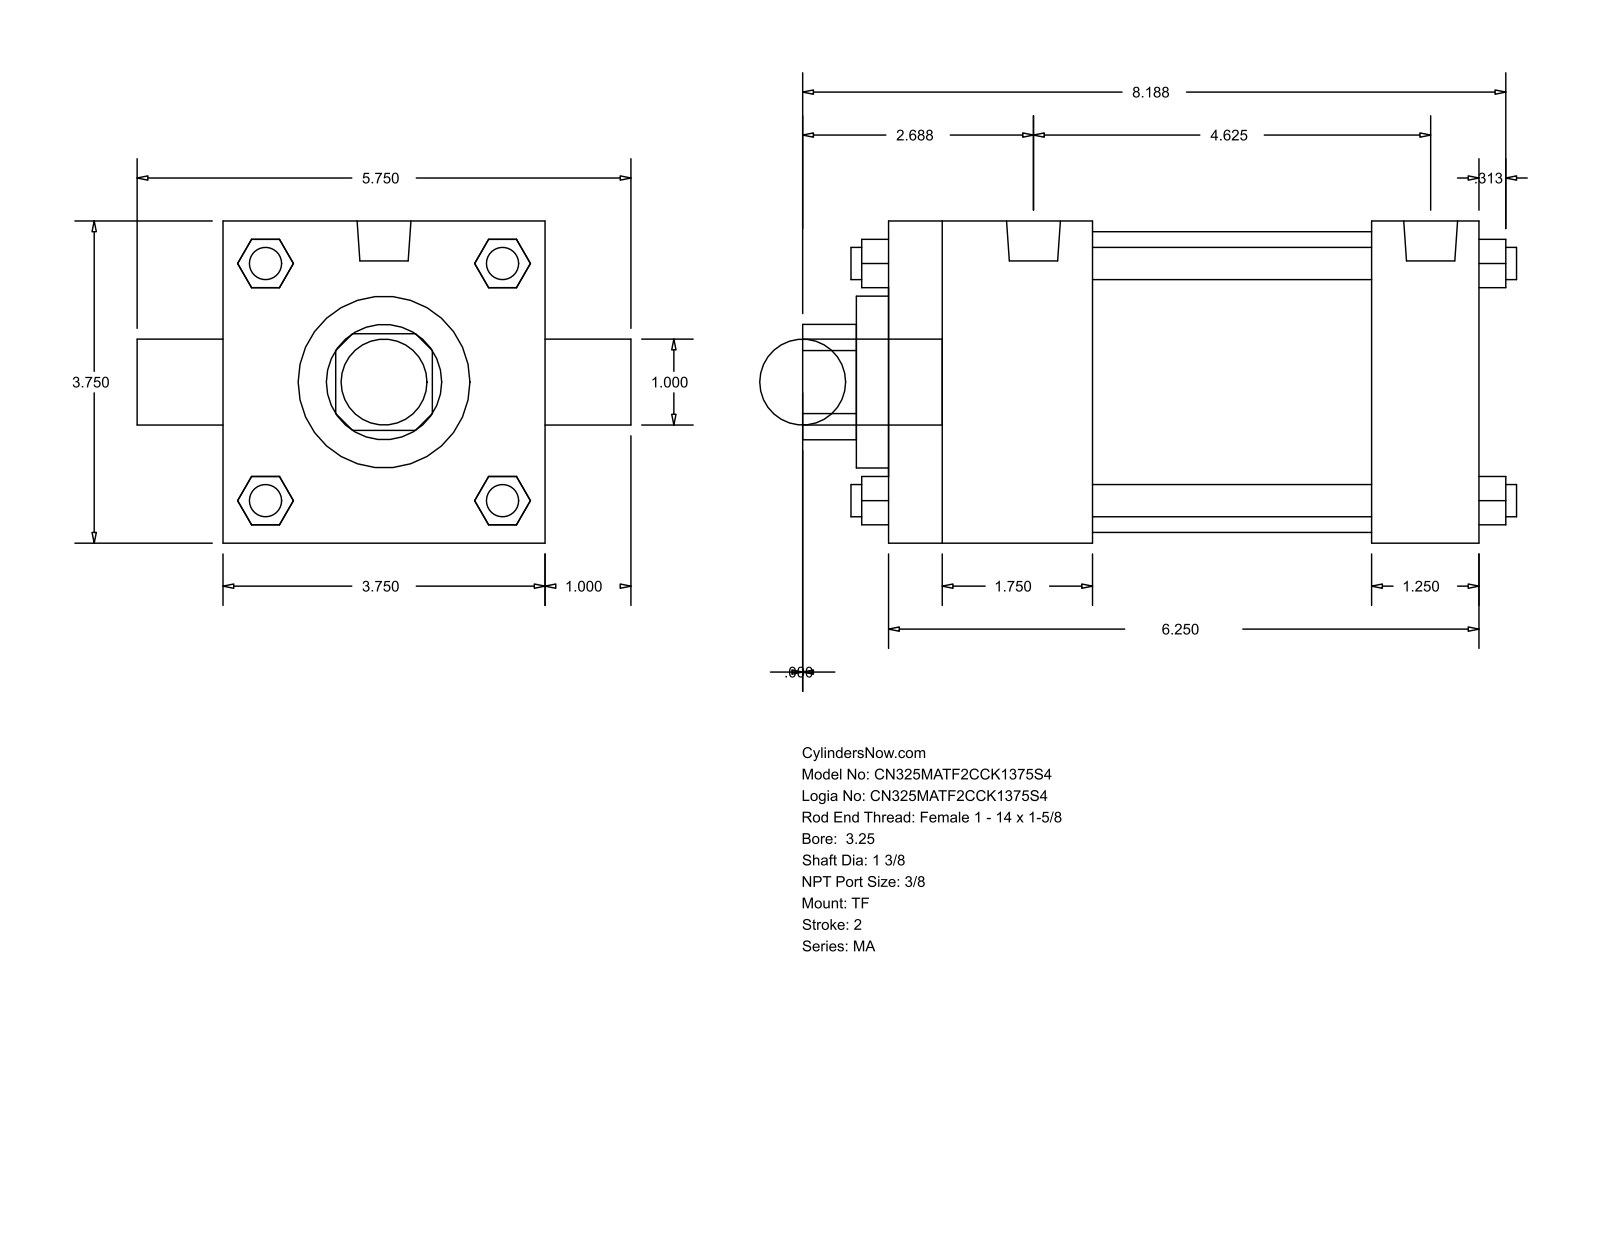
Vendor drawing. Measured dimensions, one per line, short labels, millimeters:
name: MA_TF__0325_1.375
written by: GSSL Pune (CONFIG_CONTROL_DESIGN)
unit: mm
bodies: 0 solids, 120 faces (92 planar, 28 cylindrical, 0 other)
size: 211.14 × 146.05 × 95.25
holes: 1× ⌀25.4, 1× ⌀34.92, 1× ⌀50.8, 1× ⌀88.9
bosses: 4× ⌀9.53, 3× ⌀11.11, 2× ⌀15.93, 1× ⌀25.4
rounds: 1× R17.06
face distances: 95.24, 174.63, 60.32, 142.88, 82.56, 114.31, 31.75, 9.52, 69.84, 152.4
